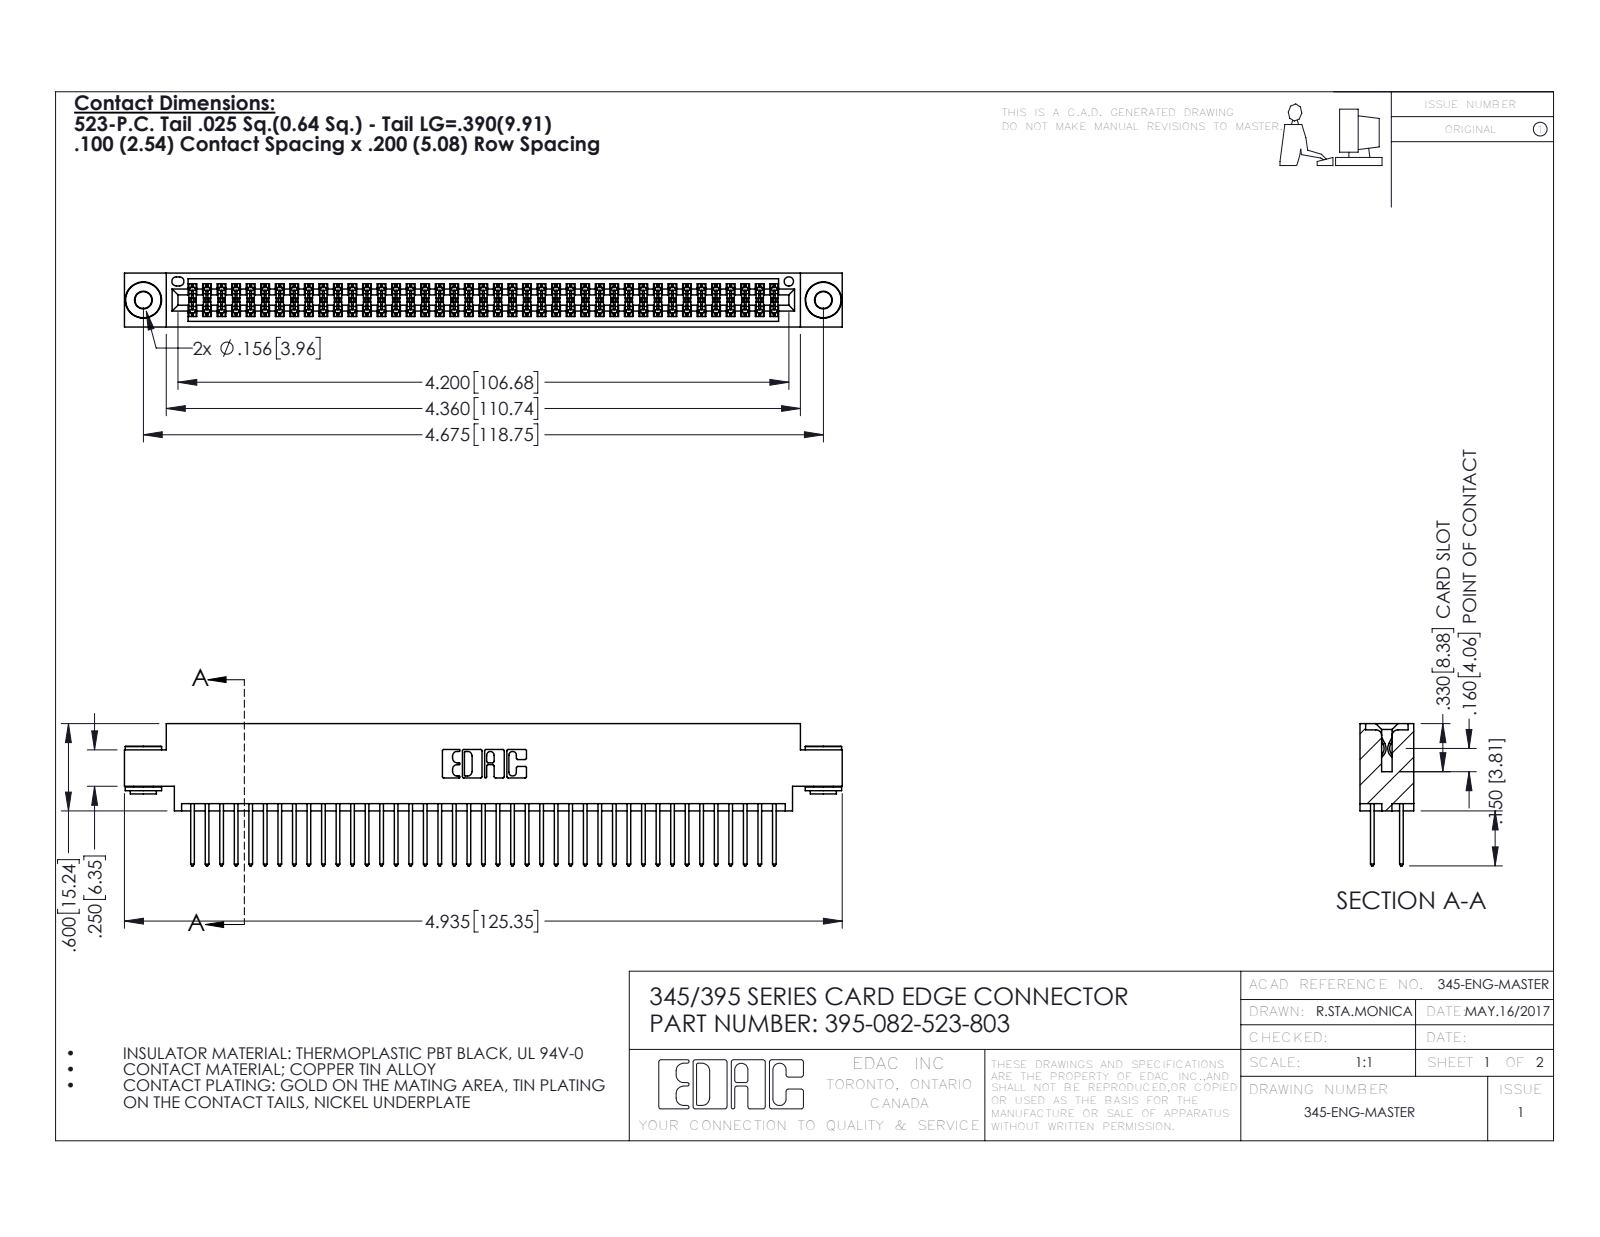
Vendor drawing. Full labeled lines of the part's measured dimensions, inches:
Part name (STEP PRODUCT): 345-292-001_345-293-123; 345 Part_0.170 Offset - 0.156 Dia-TH; 345-250-002_345-250-002-102; 395-082-523-803
STEP written by: SolidWorks 2016 (CONFIG_CONTROL_DESIGN)
Units: inches
Bodies: 85 solids, 4268 faces (2800 planar, 1460 cylindrical, 8 other)
Overall size (bounding box): 4.935 × 0.977 × 0.37
Volume: 0.747 in³ · Surface area: 29.73 in²
Round holes (diameter × count): ⌀0.116 ×2, ⌀0.156 ×2, ⌀0.064 ×1
Round bosses / shafts (diameter × count): ⌀0.25 ×2, ⌀0.18 ×2, ⌀0.136 ×2
Partial cylindrical surfaces — rounded edges, fillets, slot ends (radius × count): R0.006 ×123, R0.01 ×82, R0.01 ×22, R0.007 ×6, R0.031 ×6, R0.026 ×3, R0.014 ×2, R0.019 ×2
Main face-to-face distances: 0.072, 0.298, 0.2, 0.098, 0.272, 0.025, 0.37, 0.225, 0.175, 0.149
Hole centre spacings: 0.27, 4.439, 4.675
